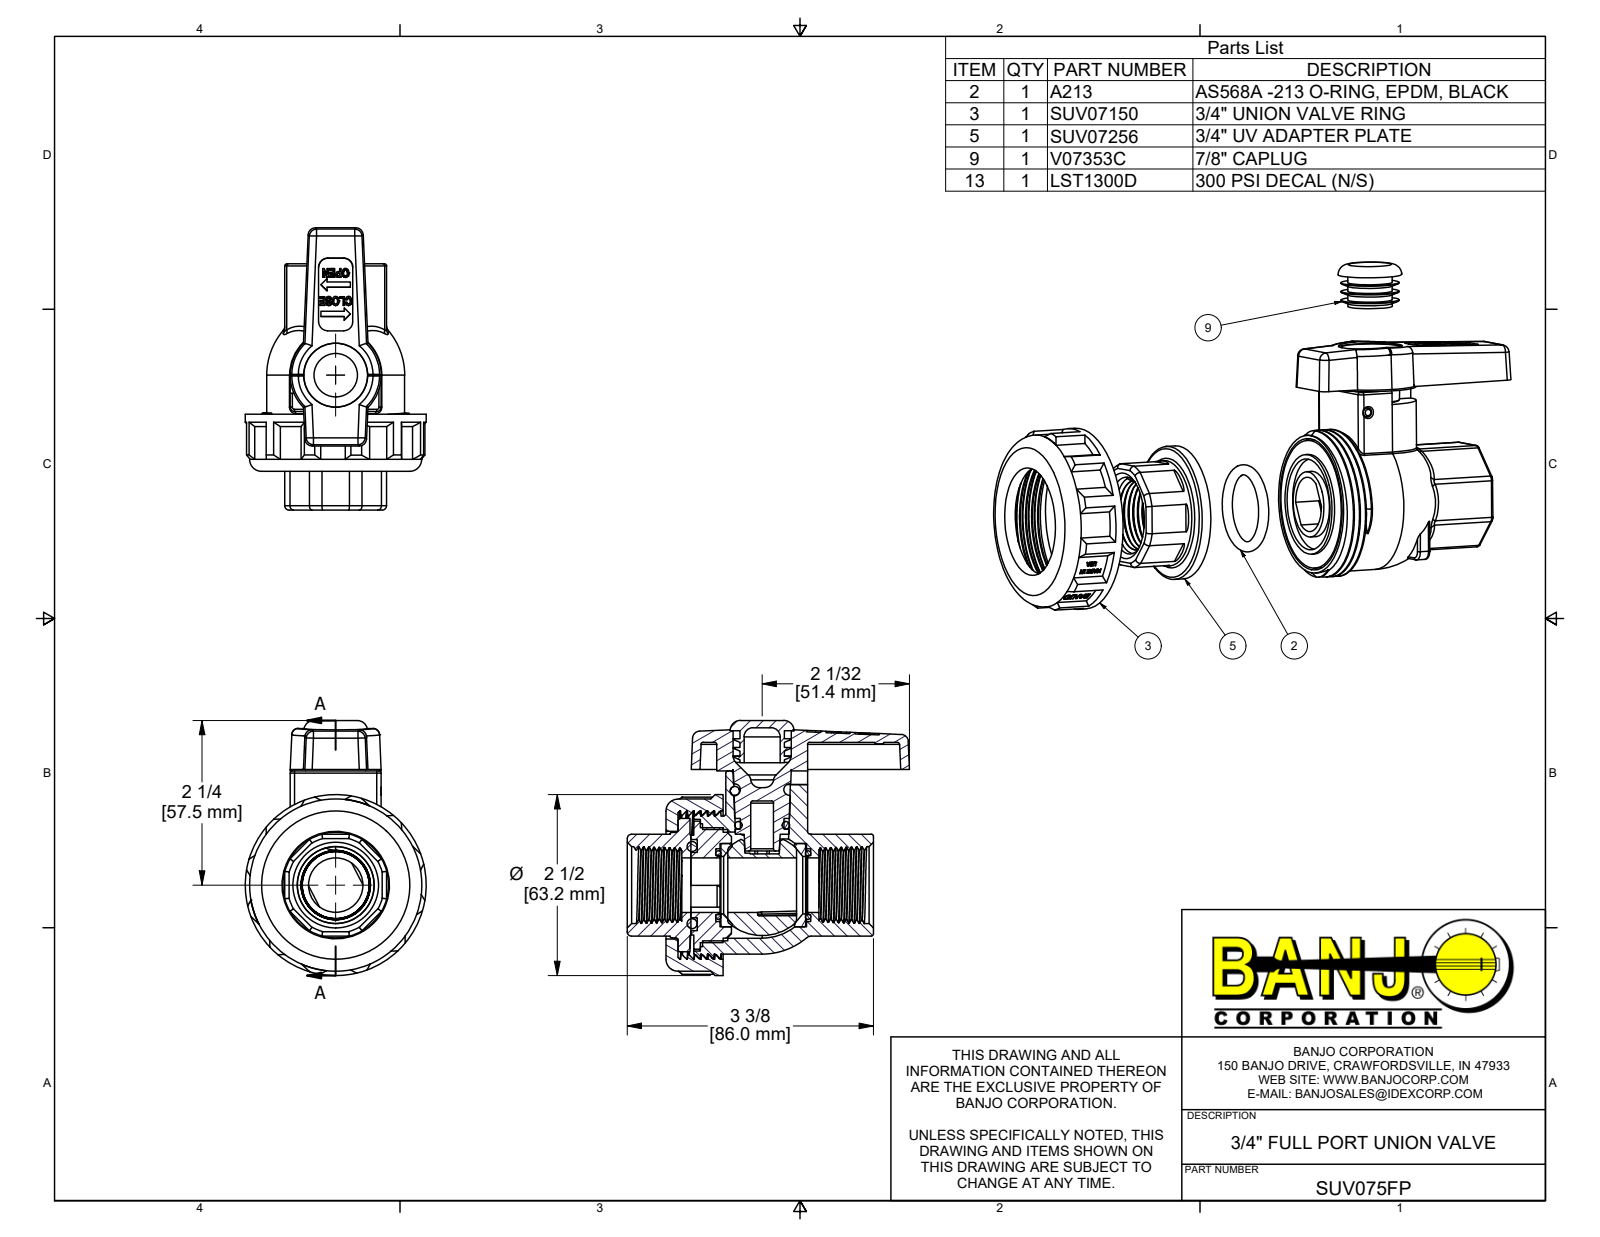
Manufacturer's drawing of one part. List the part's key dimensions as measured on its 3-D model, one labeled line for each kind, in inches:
Part name (STEP PRODUCT): SUV075FP; SUV07254; SUV07256; A213 (+8 more)
STEP written by: Autodesk Inventor 2012 (AUTOMOTIVE_DESIGN)
Units: inches
Bodies: 14 solids, 949 faces (431 planar, 203 cylindrical, 315 other)
Overall size (bounding box): 3.506 × 3.385 × 3.269
Volume: 8.101 in³ · Surface area: 109.1 in²
Round holes (diameter × count): ⌀0.75 ×2, ⌀0.128 ×1, ⌀0.313 ×1, ⌀0.494 ×1, ⌀0.79 ×1, ⌀0.802 ×1, ⌀0.88 ×1, ⌀0.936 ×1, ⌀1 ×1, ⌀1.148 ×1, ⌀1.252 ×1, ⌀1.46 ×1
Round bosses / shafts (diameter × count): ⌀2.487 ×1, ⌀2.021 ×1, ⌀1.896 ×1, ⌀1.831 ×1, ⌀1.58 ×1, ⌀1.455 ×1, ⌀1.45 ×1, ⌀1.38 ×1
Partial cylindrical surfaces — rounded edges, fillets, slot ends (radius × count): R0.03 ×25, R0.06 ×14, R0.1 ×10, R0.09 ×8, R0.125 ×6, R0.117 ×2, R0.063 ×1, R0.37 ×1
Main face-to-face distances: 0.165, 1.4, 0.443, 0.217, 0.62, 0.785, 0.343, 0.178, 0.403, 0.382
Hole centre spacings: 1.346
